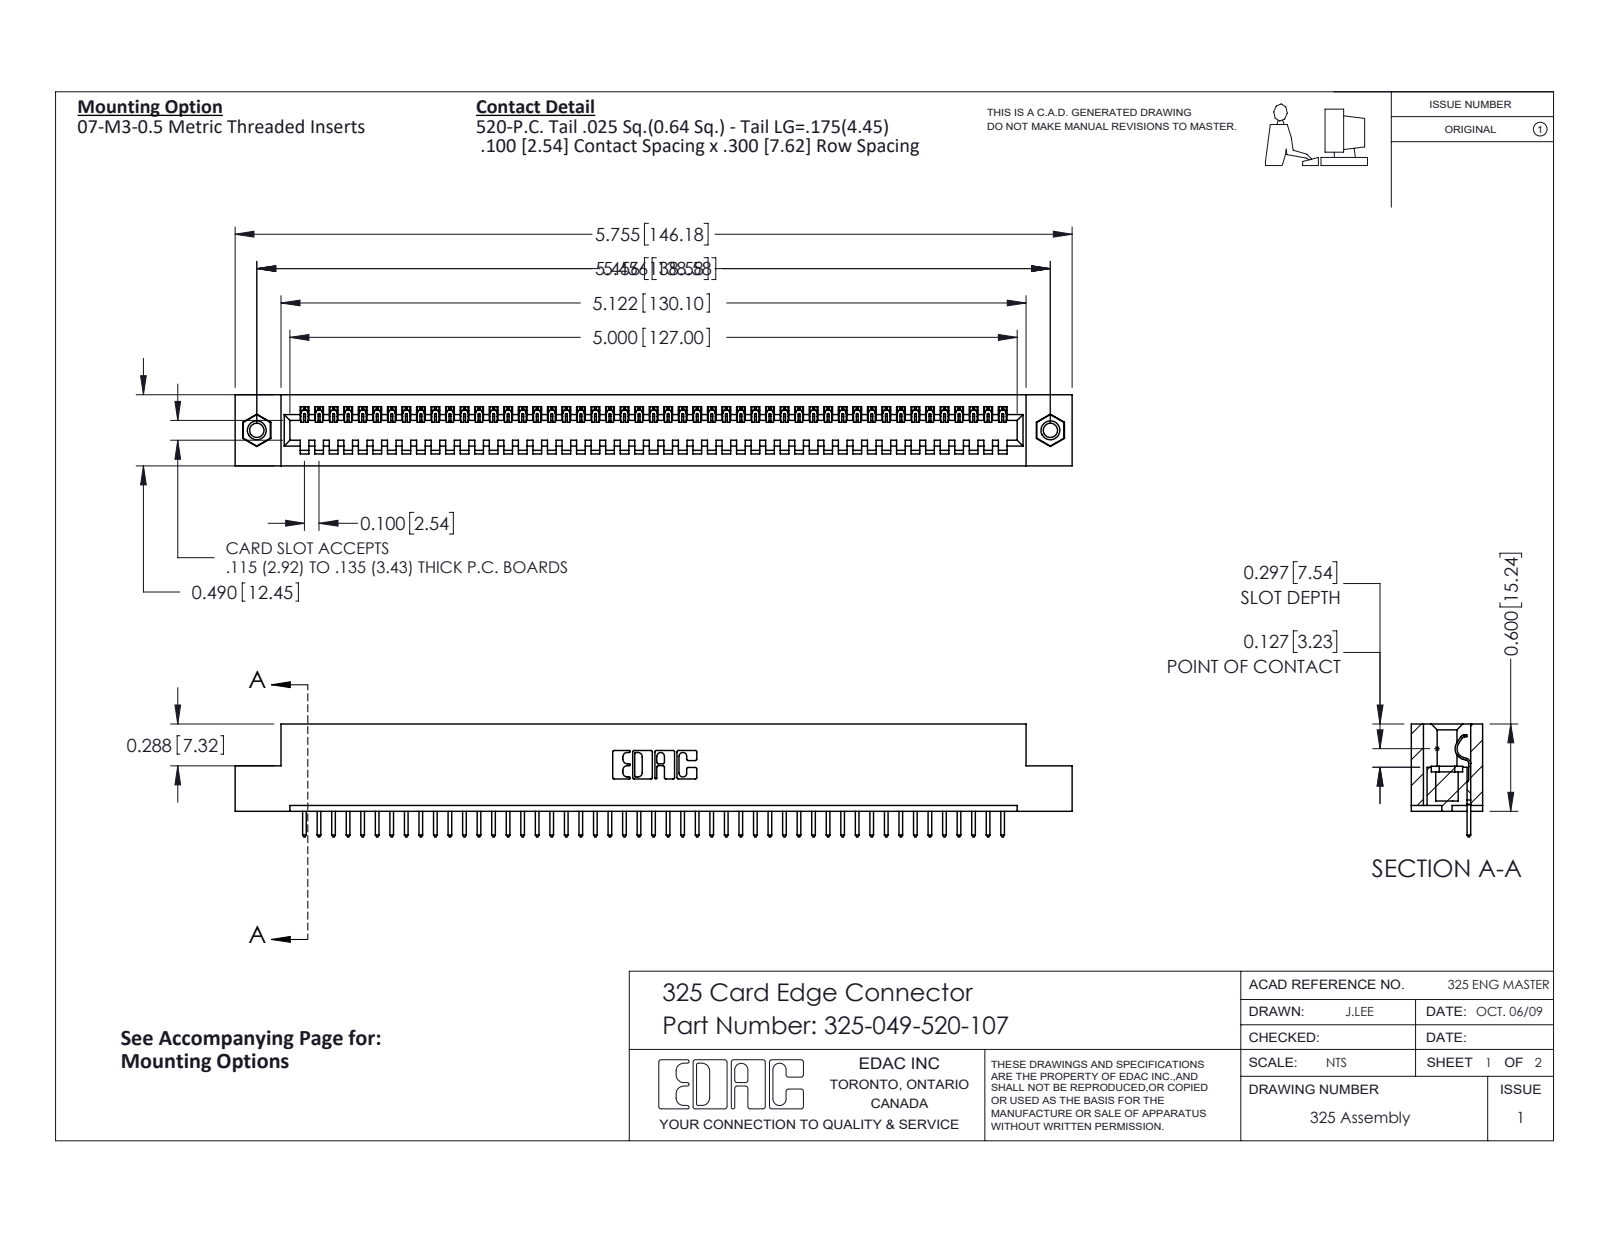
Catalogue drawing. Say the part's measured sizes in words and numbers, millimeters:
The part is named "325 Part_TI; 325-292-001_325-293-120; 345-250-001_345-250-005-103; 325-049-520-107". Its 3-D file was written by "SolidWorks 2016 (CONFIG_CONTROL_DESIGN)". It is 52 solids with 3016 faces: 2160 planar, 840 cylindrical and 16 other. Overall it measures 146.2 by 19.7 by 12.4 millimeters. Its volume is 18 470 cubic millimeters and its surface area 19 810 square millimeters. Round holes: 2 of diameter 2.5, 2 of diameter 3.2, 2 of diameter 4.1. Round bosses or shafts: 2 of diameter 3.9. Partial cylindrical surfaces (rounded edges, fillets, slot ends): 98 of radius 0.2, 98 of radius 0.3, 22 of radius 0.3, 6 of radius 0.2, 6 of radius 0.8, 3 of radius 0.7, 1 of radius 0.4, 1 of radius 0.6. The main face-to-face distances are 2.1, 10.3, 12.4, 7.6, 2.7, 9.7, 0.6, 8.3, 14.2, 6.7. The hole center spacings are 138.6.
